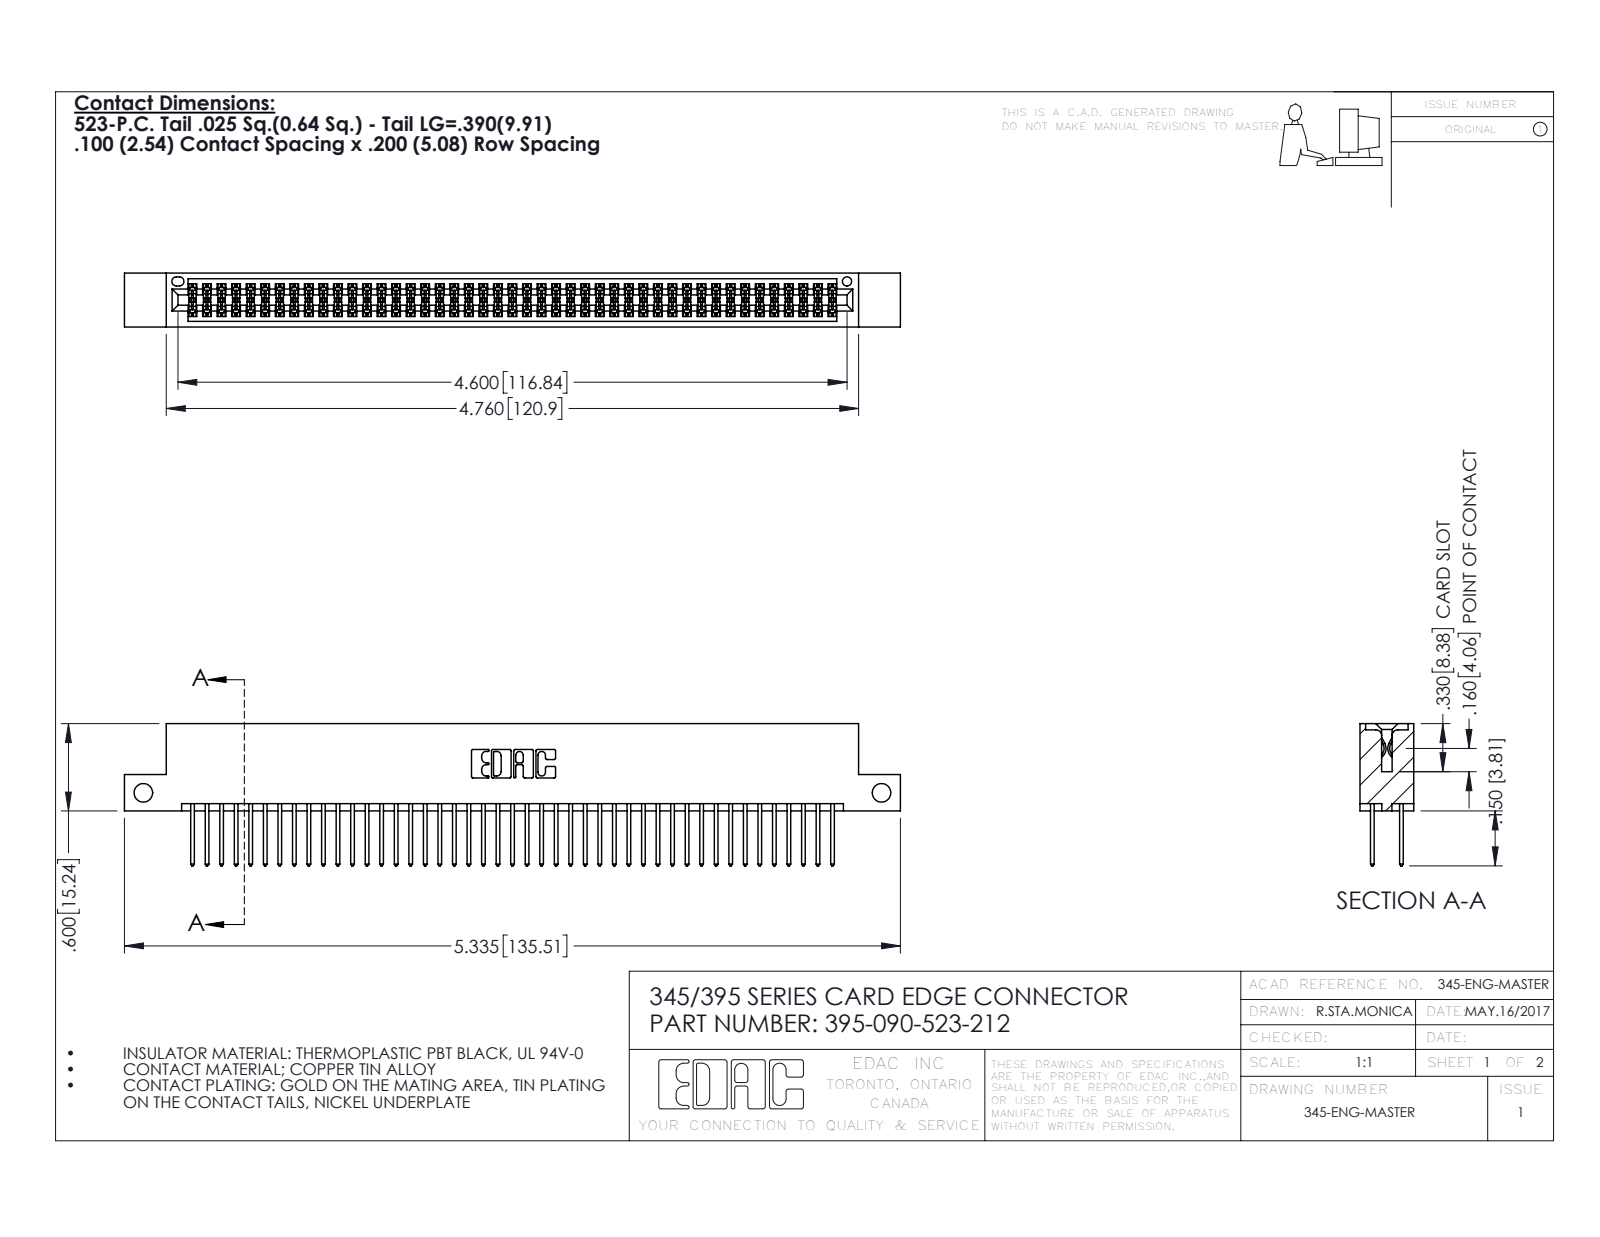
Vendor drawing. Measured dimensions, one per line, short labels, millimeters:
name: 345 Part_Flush Mounting Lugs - Side Mount; 345-292-001_345-293-123; 395-090-523-212
written by: SolidWorks 2016 (CONFIG_CONTROL_DESIGN)
unit: mm
bodies: 91 solids, 4626 faces (3050 planar, 1576 cylindrical, 0 other)
size: 135.5 × 24.8 × 9.4
volume: 13 300 mm³; area: 20 390 mm²
holes: 2× ⌀3.3, 1× ⌀1.6
rounds: 135× R0.2, 90× R0.3, 22× R0.3, 6× R0.2, 6× R0.8, 3× R0.7, 2× R0.4, 2× R0.5
face distances: 7.6, 1.8, 5.1, 2.5, 6.9, 0.6, 9.4, 5.7, 4.4, 3.8
hole spacings: 128.9
